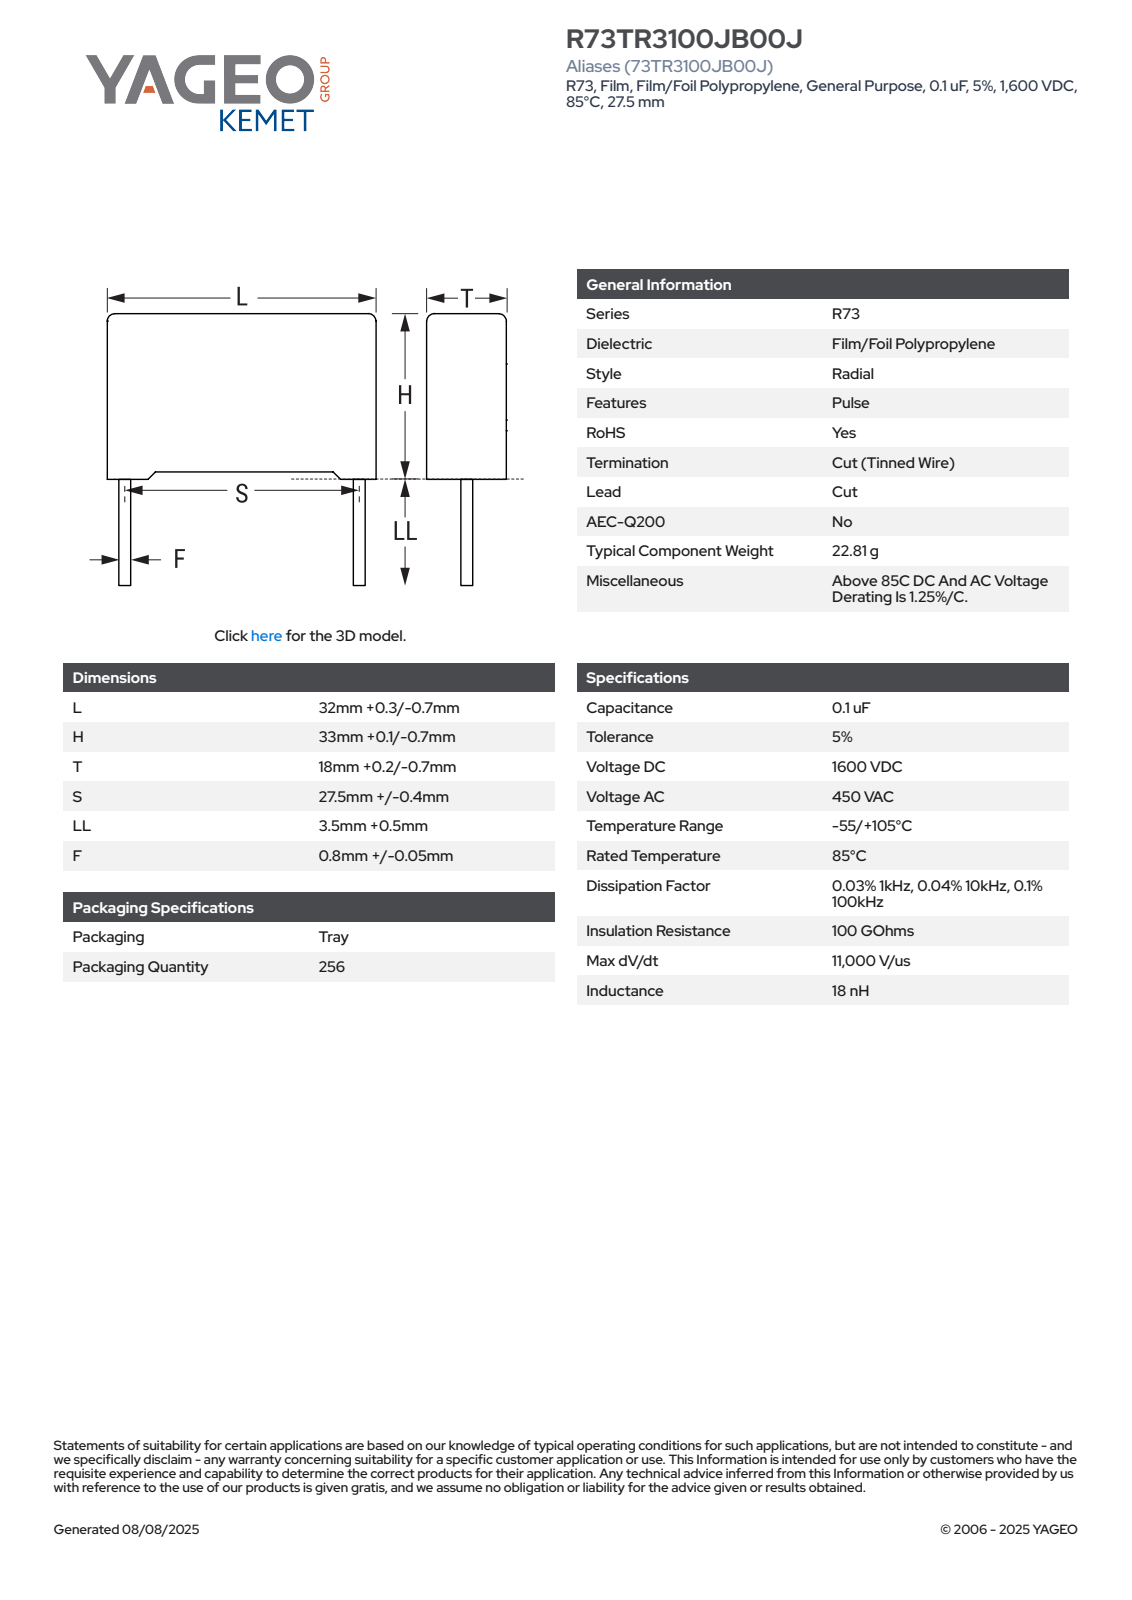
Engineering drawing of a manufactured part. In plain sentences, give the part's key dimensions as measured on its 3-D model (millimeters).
The part is named "CFR_RB2_32X33X18_L32.3H33.1T18.2S27.5LL4F0.85". Its 3-D file was written by "SolidWorks 2021 (AUTOMOTIVE_DESIGN)". It is 4 solids with 85 faces: 77 planar, 8 cylindrical and 0 other. Overall it measures 37.1 by 32.3 by 18.2 millimeters. Its volume is 18 893 cubic millimeters and its surface area 4 589 square millimeters. Round bosses or shafts: 2 of diameter 0.85. Partial cylindrical surfaces (rounded edges, fillets, slot ends): 4 of radius 0.5. The main face-to-face distances are 18.2, 32.3, 31.96, 0.39, 32.35, 0.75, 1.14, 33.1, 1.08, 31.22.
